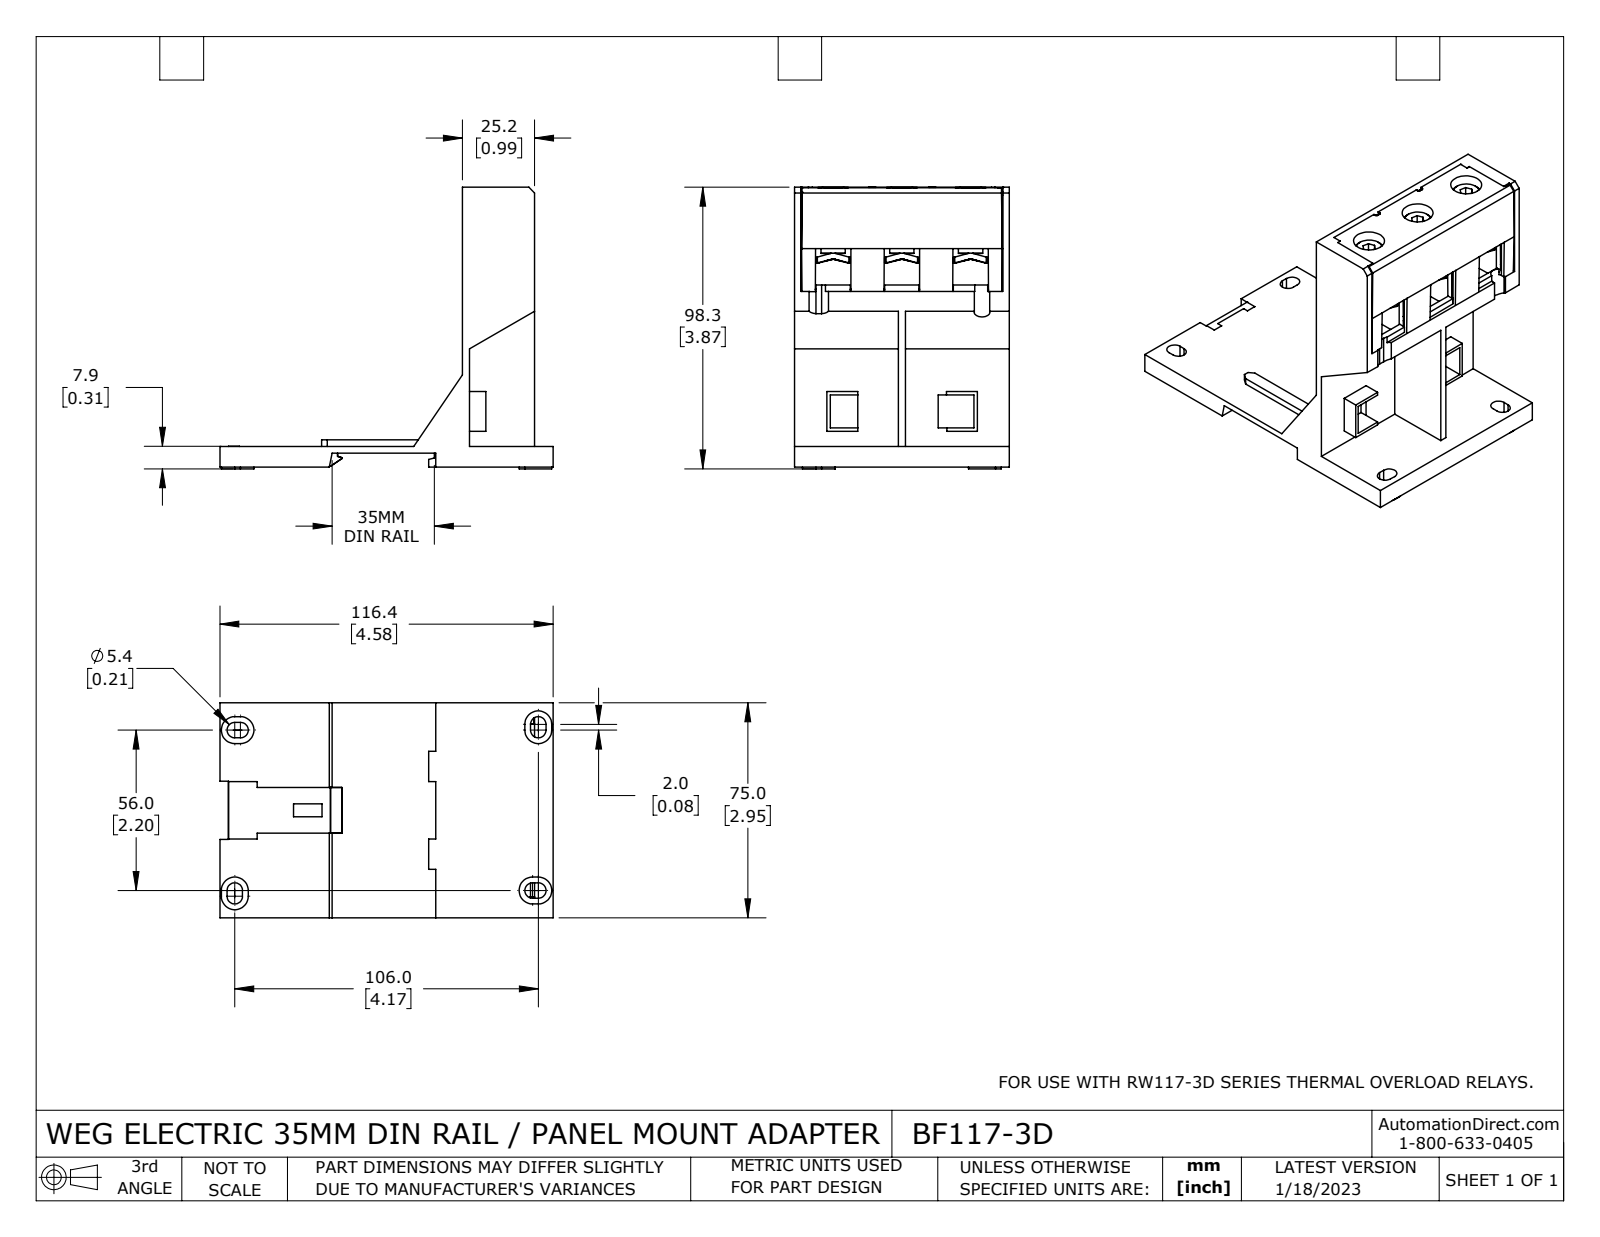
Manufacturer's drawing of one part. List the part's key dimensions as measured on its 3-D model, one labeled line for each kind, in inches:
Part name (STEP PRODUCT): BF117-3D
STEP written by: SolidWorks 2021 (CONFIG_CONTROL_DESIGN)
Units: inches
Bodies: 12 solids, 605 faces (459 planar, 114 cylindrical, 32 other)
Overall size (bounding box): 4.582 × 3.87 × 2.953
Volume: 7.825 in³ · Surface area: 114.5 in²
Round holes (diameter × count): ⌀0.34 ×3, ⌀0.425 ×3
Round bosses / shafts (diameter × count): ⌀0.394 ×3, ⌀0.335 ×3, ⌀0.507 ×2
Partial cylindrical surfaces — rounded edges, fillets, slot ends (radius × count): R0.02 ×12, R0.024 ×8, R0.106 ×8, R0.185 ×8, R0.075 ×6, R0.197 ×6, R0.059 ×3, R0.138 ×3
Main face-to-face distances: 0.098, 0.283, 0.945, 0.091, 0.193, 0.079, 0.374, 0.659, 0.285, 0.571
Hole centre spacings: 0.945, 1.89
